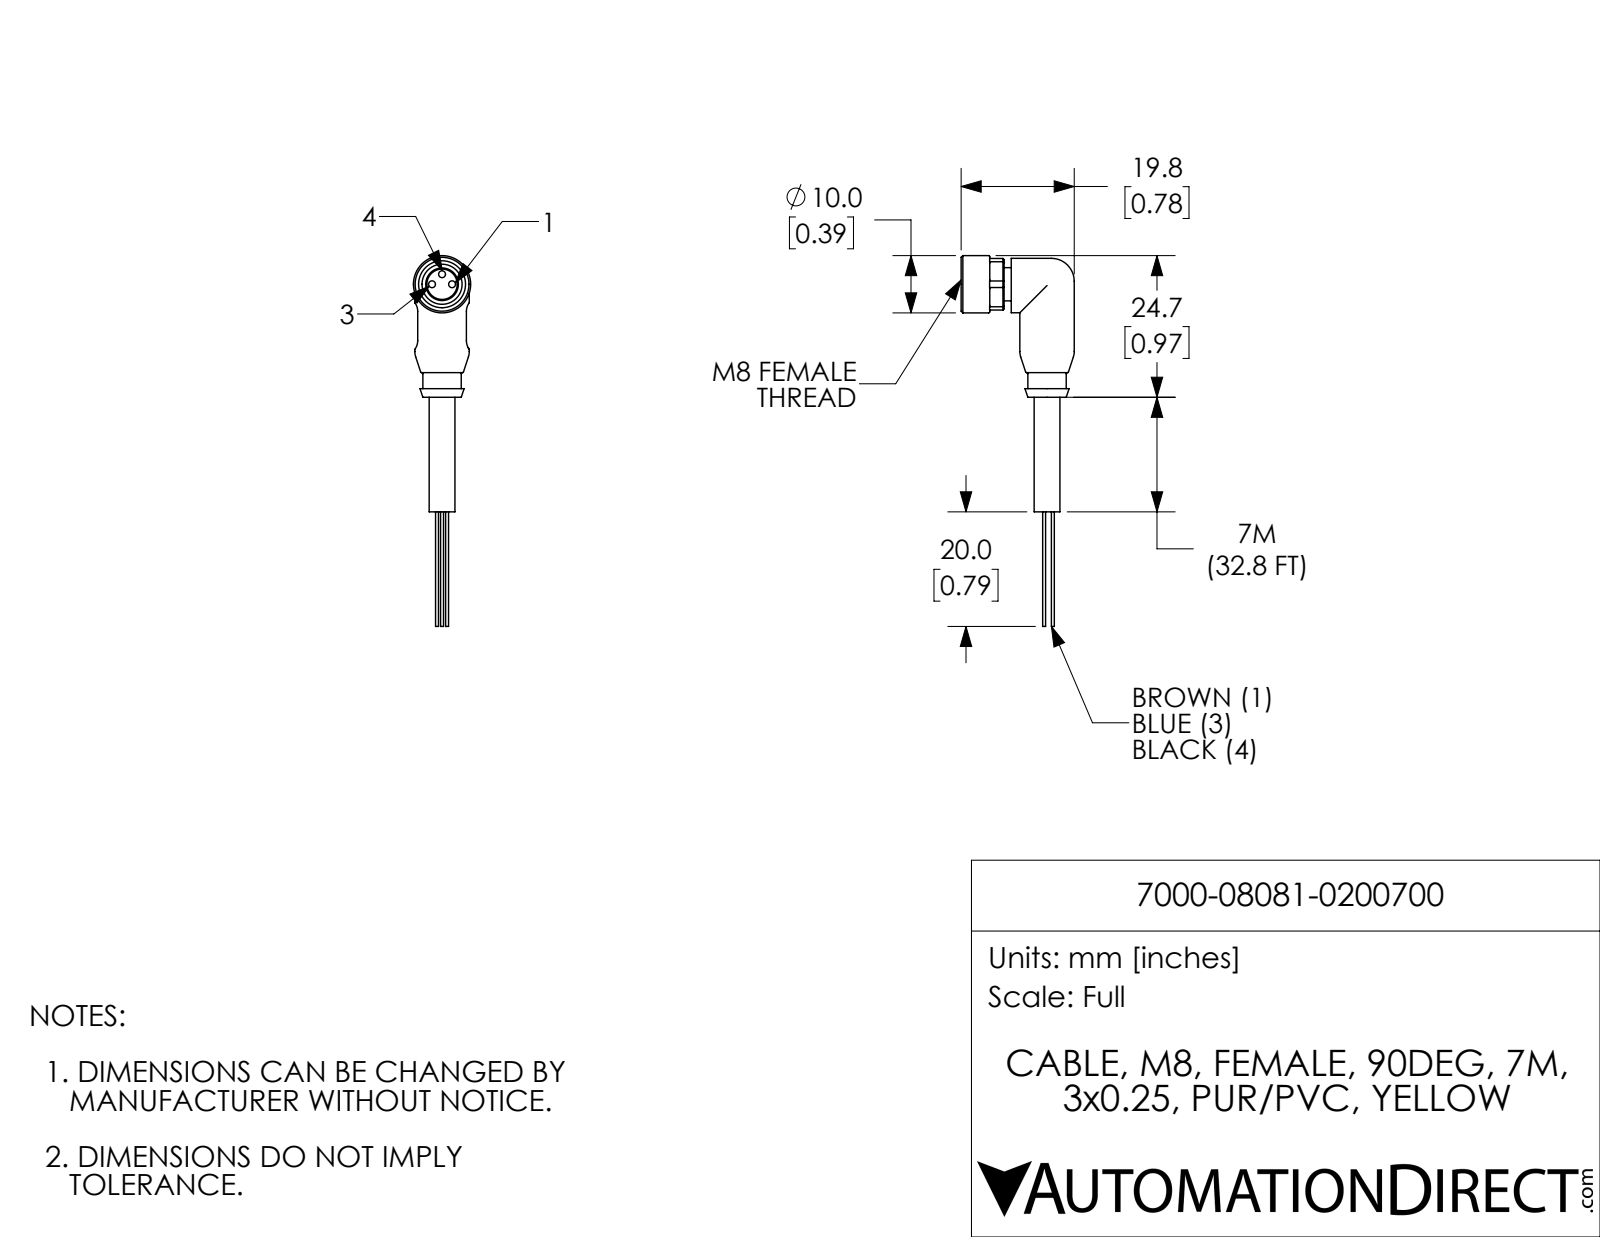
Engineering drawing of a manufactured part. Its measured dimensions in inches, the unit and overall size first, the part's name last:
Units: inches
Overall size (bounding box): 2.548 × 0.778 × 0.394
Round holes (diameter × count): ⌀0.047 ×3, ⌀0.276 ×1
Round bosses / shafts (diameter × count): ⌀0.02 ×3, ⌀0.374 ×2, ⌀0.394 ×1, ⌀0.264 ×1, ⌀0.228 ×1, ⌀0.224 ×1, ⌀0.177 ×1
Partial cylindrical surfaces — rounded edges, fillets, slot ends (radius × count): R0.008 ×4, R0.098 ×4, R0.193 ×1
Main face-to-face distances: 0.049, 0.354, 0.059, 0.335, 0.028, 0.268, 0.317, 0.295, 0.344, 0.787
Hole centre spacings: 0.069, 0.097, 0.138
Volume: 0.147 in³ · Surface area: 2.844 in²
Bodies: 1 solid, 107 faces (35 planar, 43 cylindrical, 29 other)
Part name (STEP PRODUCT): 7000-08081-0200700
STEP written by: SolidWorks 2017 (AUTOMOTIVE_DESIGN)
